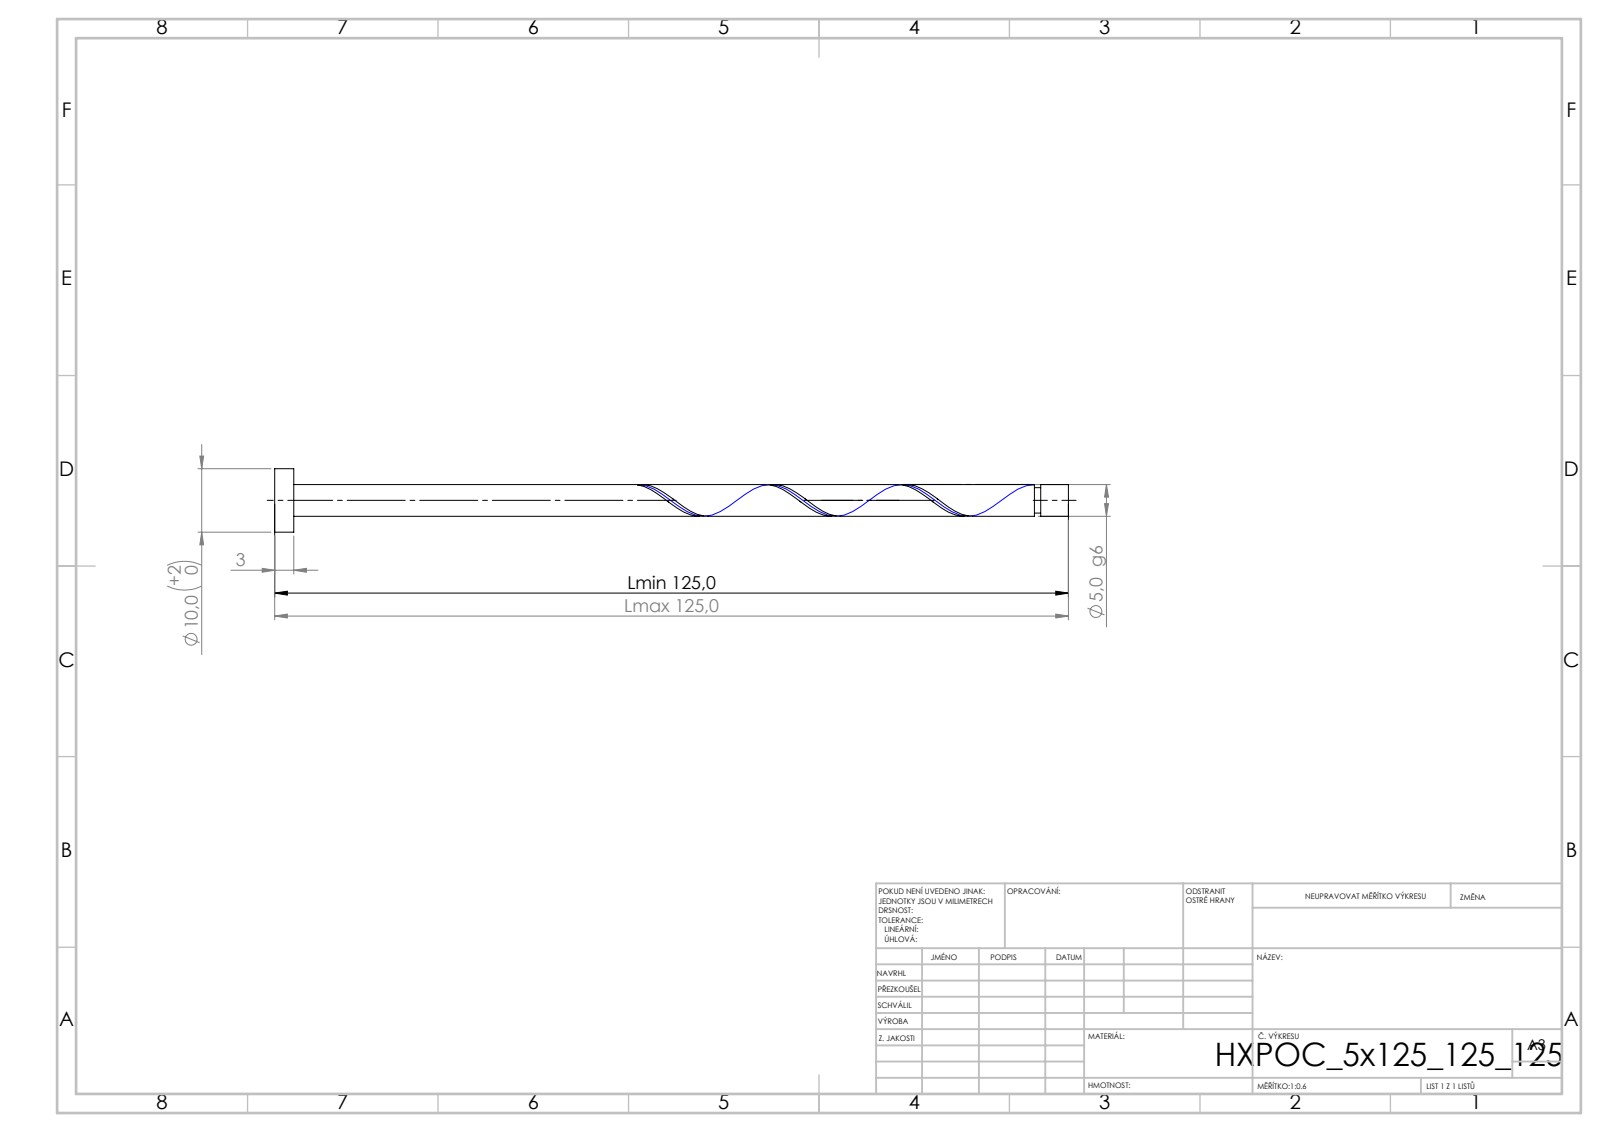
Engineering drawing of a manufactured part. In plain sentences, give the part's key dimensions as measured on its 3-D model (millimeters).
Its 3-D file was written by "SolidWorks 2019 (CONFIG_CONTROL_DESIGN)". It is 1 solid with 21 faces: 6 planar, 14 cylindrical and 1 other. Overall it measures 125 by 10 by 10 millimeters. Its volume is 2 601 cubic millimeters and its surface area 2 219 square millimeters. Round bosses or shafts: 1 of diameter 10, 1 of diameter 5, 1 of diameter 4. The main face-to-face distances are 3, 125, 122, 120.65, 117.65, 4.35, 119.65, 116.65, 1, 5.35.
